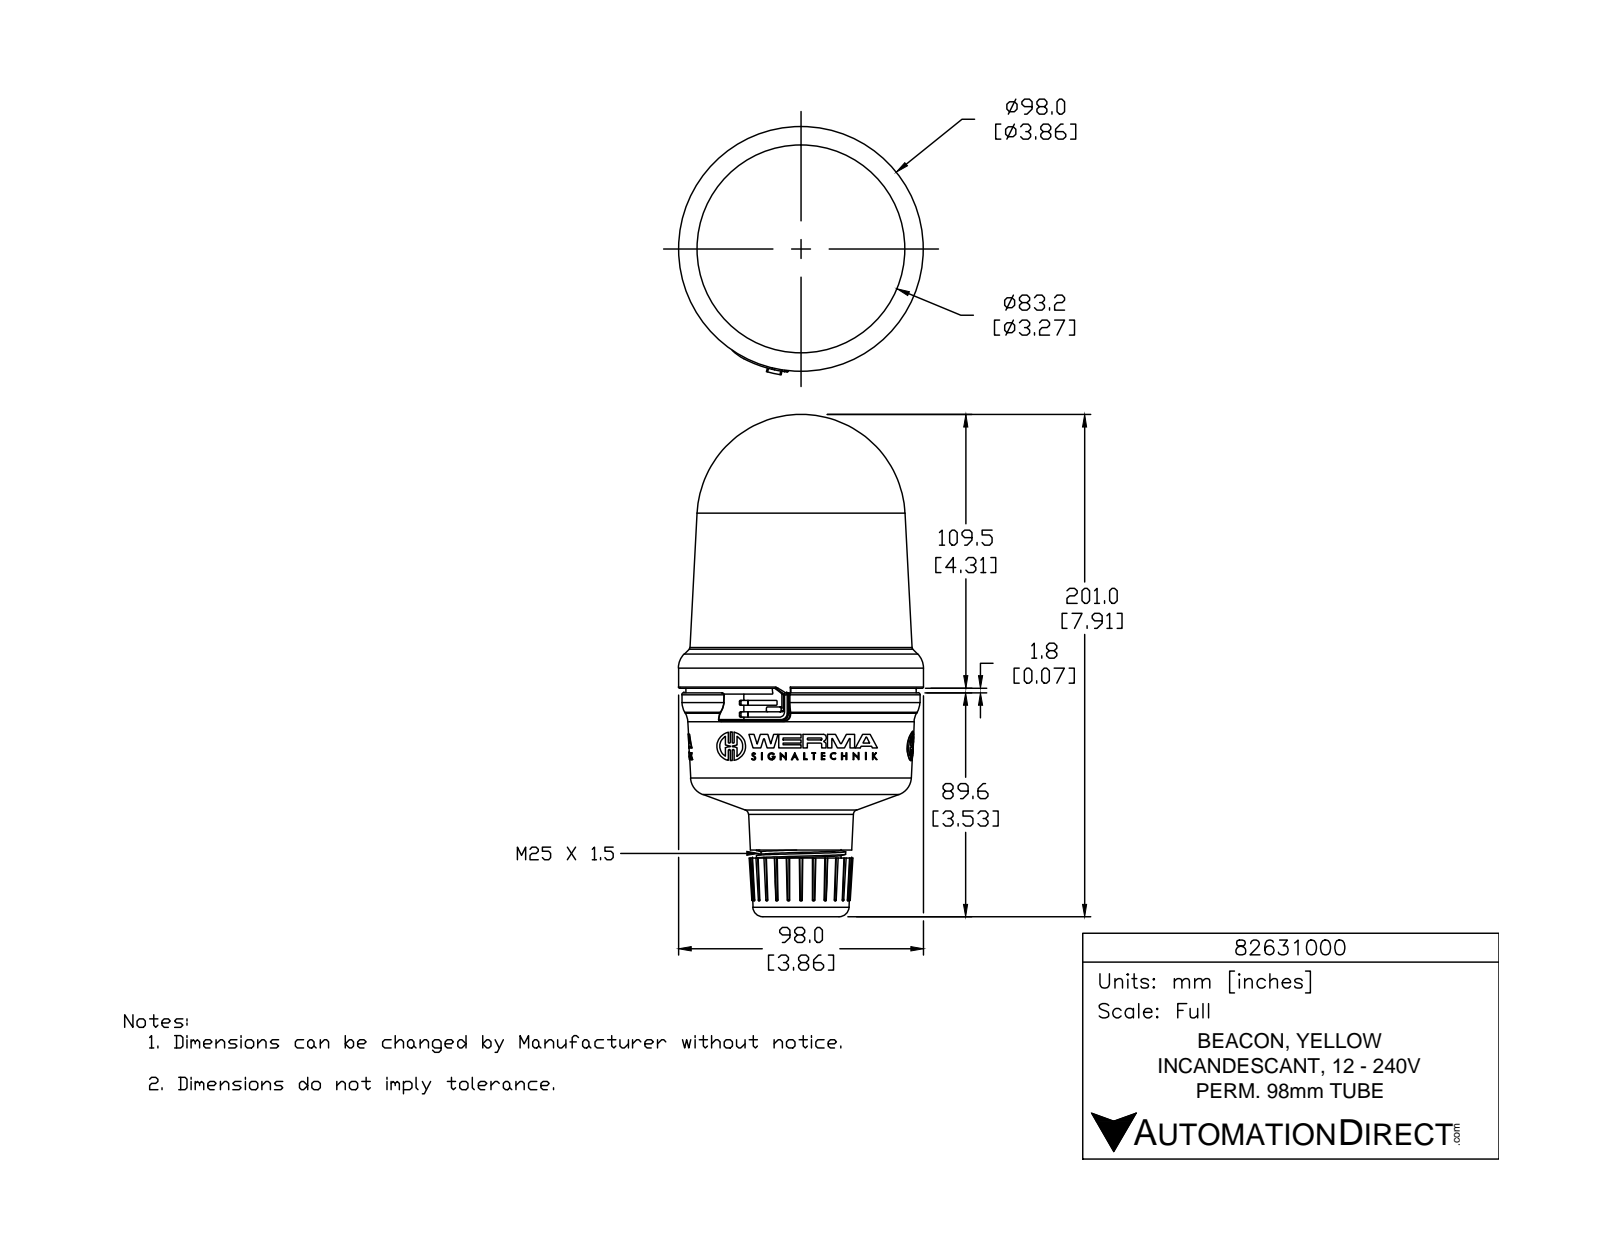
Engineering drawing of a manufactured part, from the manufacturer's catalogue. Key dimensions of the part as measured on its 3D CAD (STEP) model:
Part name (STEP PRODUCT): 82631000
STEP written by: SolidWorks 2015 (AUTOMOTIVE_DESIGN)
Units: inches
Bodies: 1 solid, 1006 faces (554 planar, 189 cylindrical, 263 other)
Overall size (bounding box): 7.914 × 3.912 × 3.858
Volume: 54.7 in³ · Surface area: 91.39 in²
Round holes (diameter × count): ⌀0.078 ×3, ⌀1.013 ×1, ⌀1.024 ×1
Round bosses / shafts (diameter × count): ⌀0.452 ×3, ⌀0.113 ×3, ⌀3.858 ×1, ⌀1.409 ×1, ⌀1.261 ×1
Partial cylindrical surfaces — rounded edges, fillets, slot ends (radius × count): R0.02 ×12, R0.007 ×9, R0.007 ×6, R0.016 ×6, R0.016 ×6, R0.016 ×6, R0.262 ×6, R0.006 ×3
Main face-to-face distances: 2.214, 0.462, 2.676, 0.335, 0.127, 2.548, 2.603, 2.476, 2.141, 0.073
